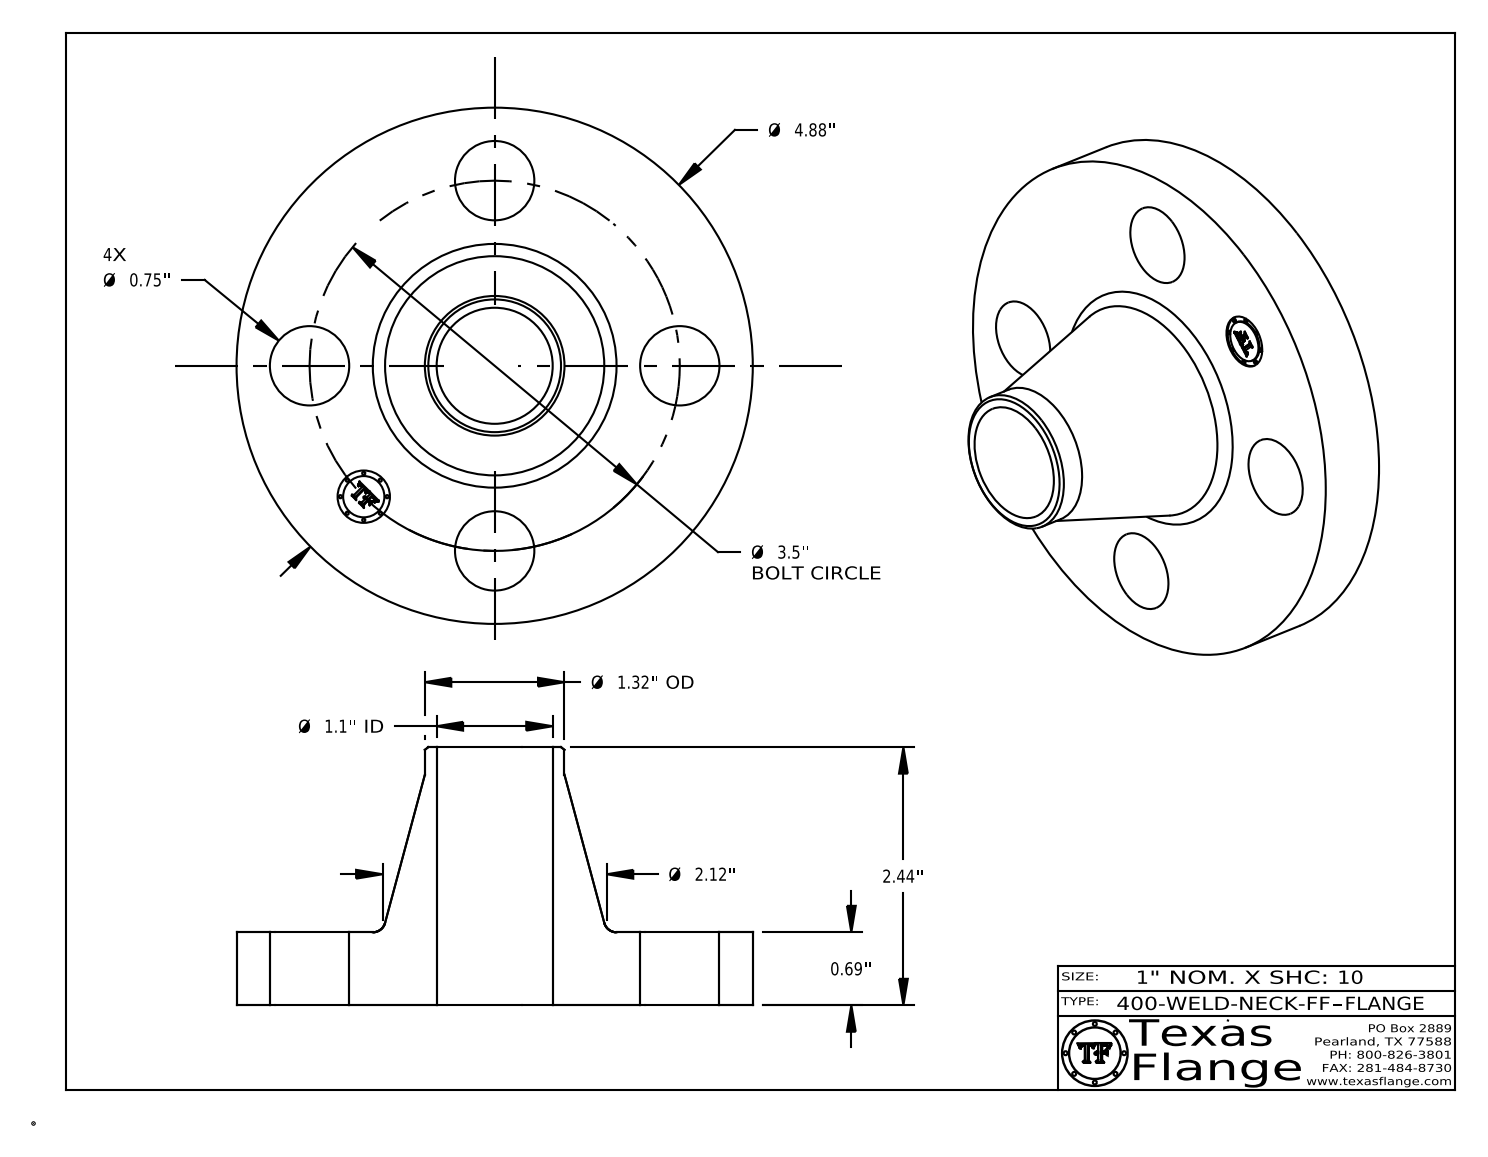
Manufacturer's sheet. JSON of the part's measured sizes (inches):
{"part_name": "400-WELD-NECK-FF", "step_written_by": "CATIA V5 STEP AP214 (AUTOMOTIVE_DESIGN)", "units": "inches", "bodies": {"solids": 1, "faces": 408, "planar": 368, "cylindrical": 34, "other": 6}, "overall_size": [4.88, 4.88, 2.44], "volume_in3": 13.27, "surface_area_in2": 64.57, "round_holes": [[0.75, 4], [0.495, 1], [1.097, 1]], "round_bosses_or_shafts": [[0.03, 8], [4.88, 1], [1.32, 1], [0.39, 1]], "face_to_face_distances": [0.69, 2.44, 1.75, 0.015, 0.675, 1.765, 0.148, 0.145, 0.027, 0.096], "hole_center_spacings": [1.75, 2.475, 1.339, 3.233, 3.5]}
